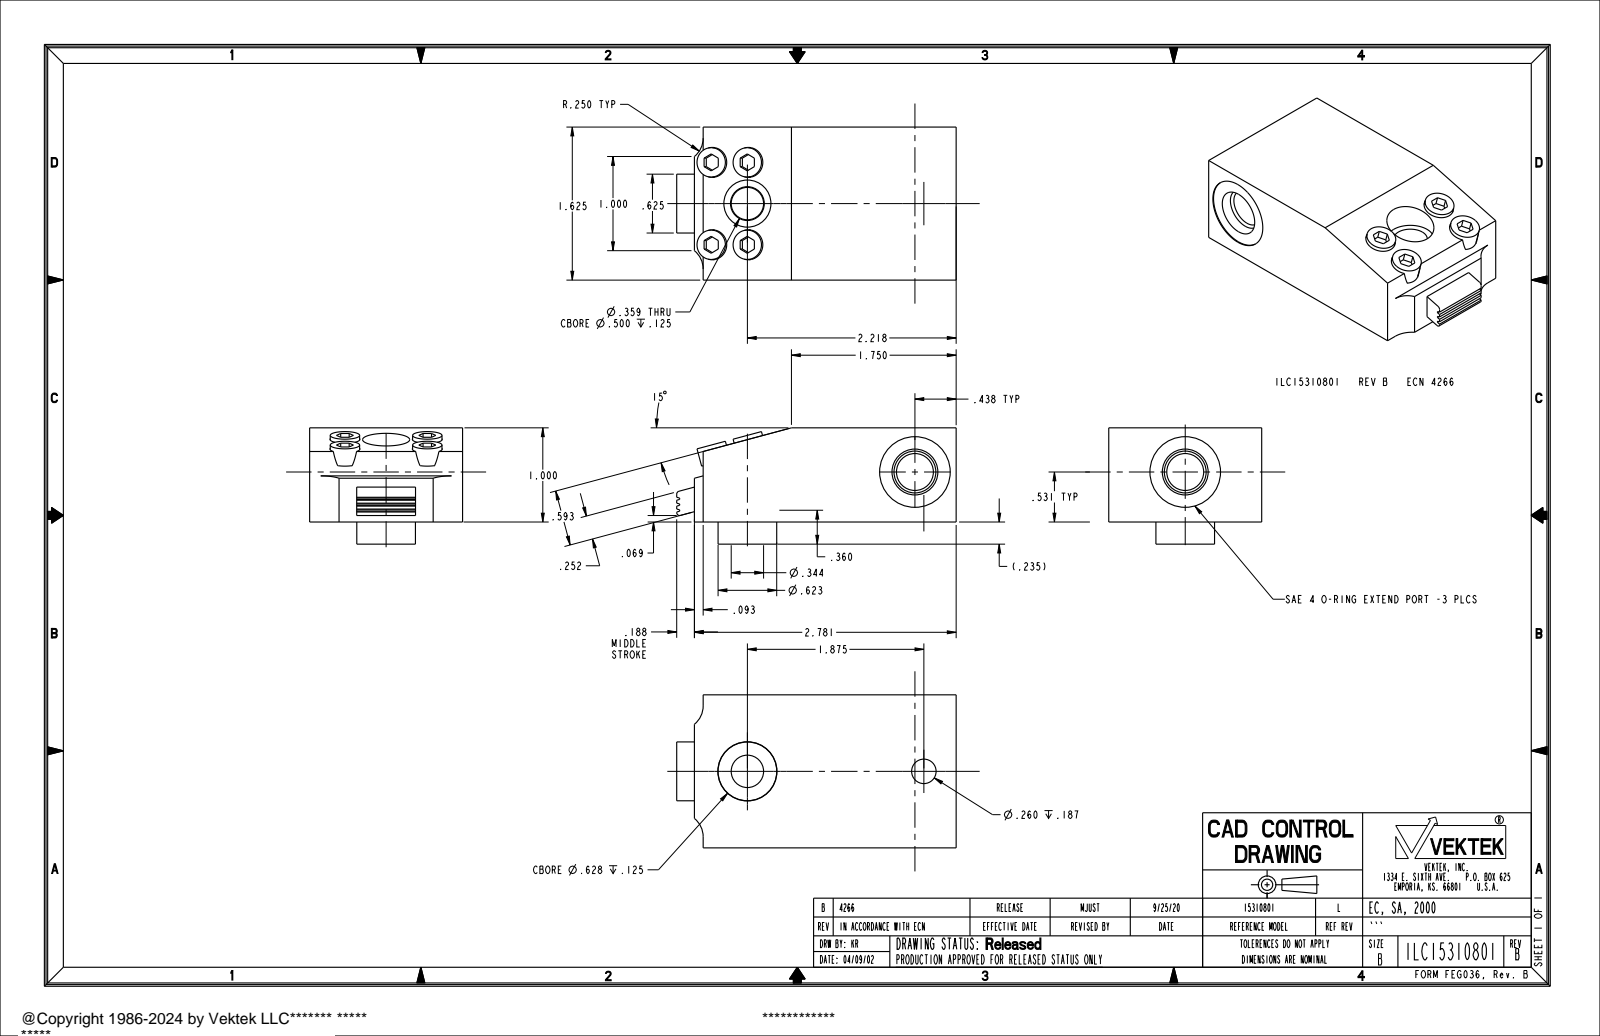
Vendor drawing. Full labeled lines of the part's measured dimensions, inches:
Part name (STEP PRODUCT): ILC15310801
STEP written by: PRO/ENGINEER BY PARAMETRIC TECHNOLOGY CORPORATION, 2017170 (AUTOMOTIVE_DESIGN)
Units: inches
Bodies: 1 solid, 129 faces (75 planar, 42 cylindrical, 12 other)
Overall size (bounding box): 2.969 × 1.625 × 1.235
Volume: 3.926 in³ · Surface area: 23.28 in²
Round holes (diameter × count): ⌀0.318 ×4, ⌀0.392 ×2, ⌀0.75 ×2, ⌀0.26 ×1, ⌀0.344 ×1, ⌀0.359 ×1, ⌀0.5 ×1, ⌀0.628 ×1
Round bosses / shafts (diameter × count): ⌀0.312 ×4, ⌀0.623 ×1
Partial cylindrical surfaces — rounded edges, fillets, slot ends (radius × count): R0.031 ×2, R0.25 ×2
Main face-to-face distances: 1, 1.625, 1.615, 2.688, 0.55, 0.093, 2.781, 0.1, 1.605, 2.681
Hole centre spacings: 0.397, 0.875, 0.961, 1.875
